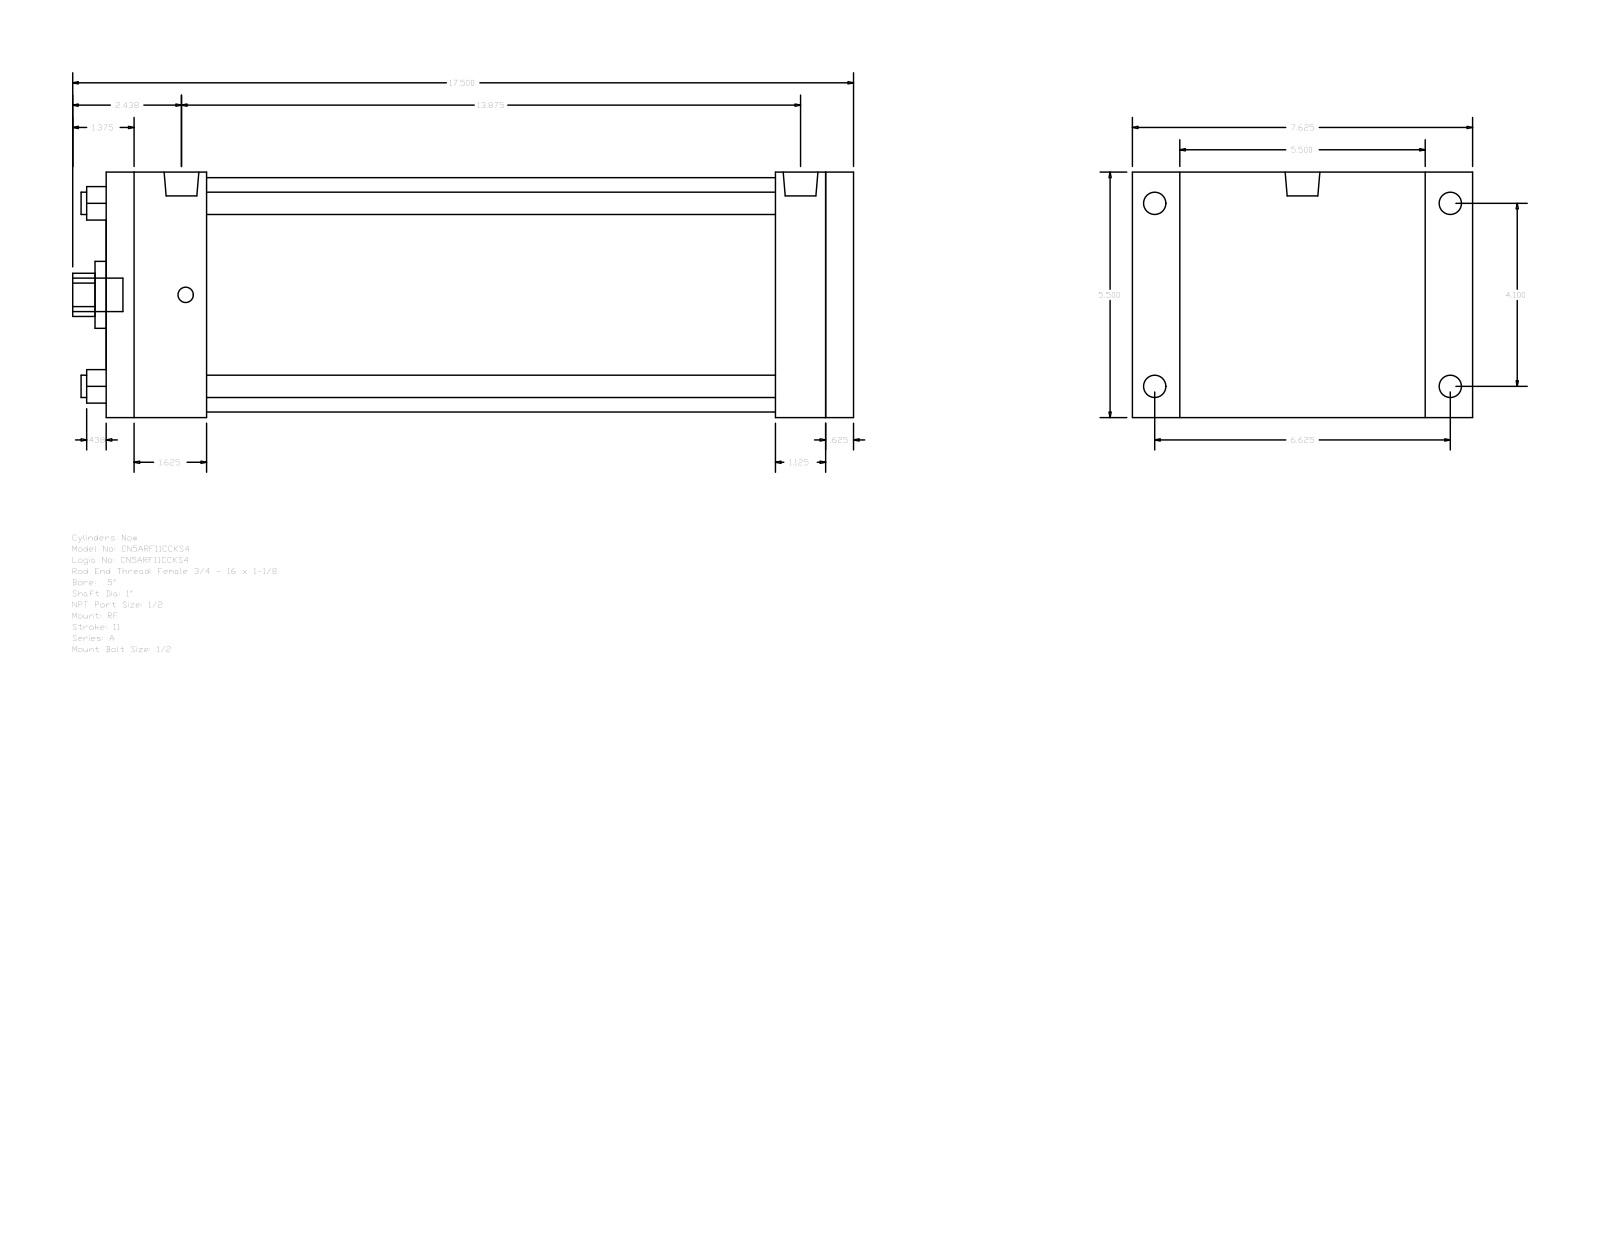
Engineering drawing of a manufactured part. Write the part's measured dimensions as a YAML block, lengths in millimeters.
part_name: "A_RF__0500_1"
step_written_by: "GSSL Pune (CONFIG_CONTROL_DESIGN)"
units: millimeters
bodies: {solids: 0, faces: 92, planar: 64, cylindrical: 28, other: 0}
overall_size: [444.5, 193.68, 139.7]
round_holes:
  - {diameter: 12.7, count: 4}
  - {diameter: 25.4, count: 1}
  - {diameter: 38.1, count: 1}
  - {diameter: 133.35, count: 1}
round_bosses_or_shafts:
  - {diameter: 12.7, count: 4}
  - {diameter: 8.73, count: 4}
  - {diameter: 19.77, count: 2}
  - {diameter: 19.05, count: 1}
partial_cylinders:
  - {radius: 12.29, count: 1}
face_to_face_distances: [139.7, 425.45, 409.57, 15.88, 28.57, 57.15, 352.42, 368.3, 381, 323.85]
hole_center_spacings: [73.64, 104.14, 147.28]
